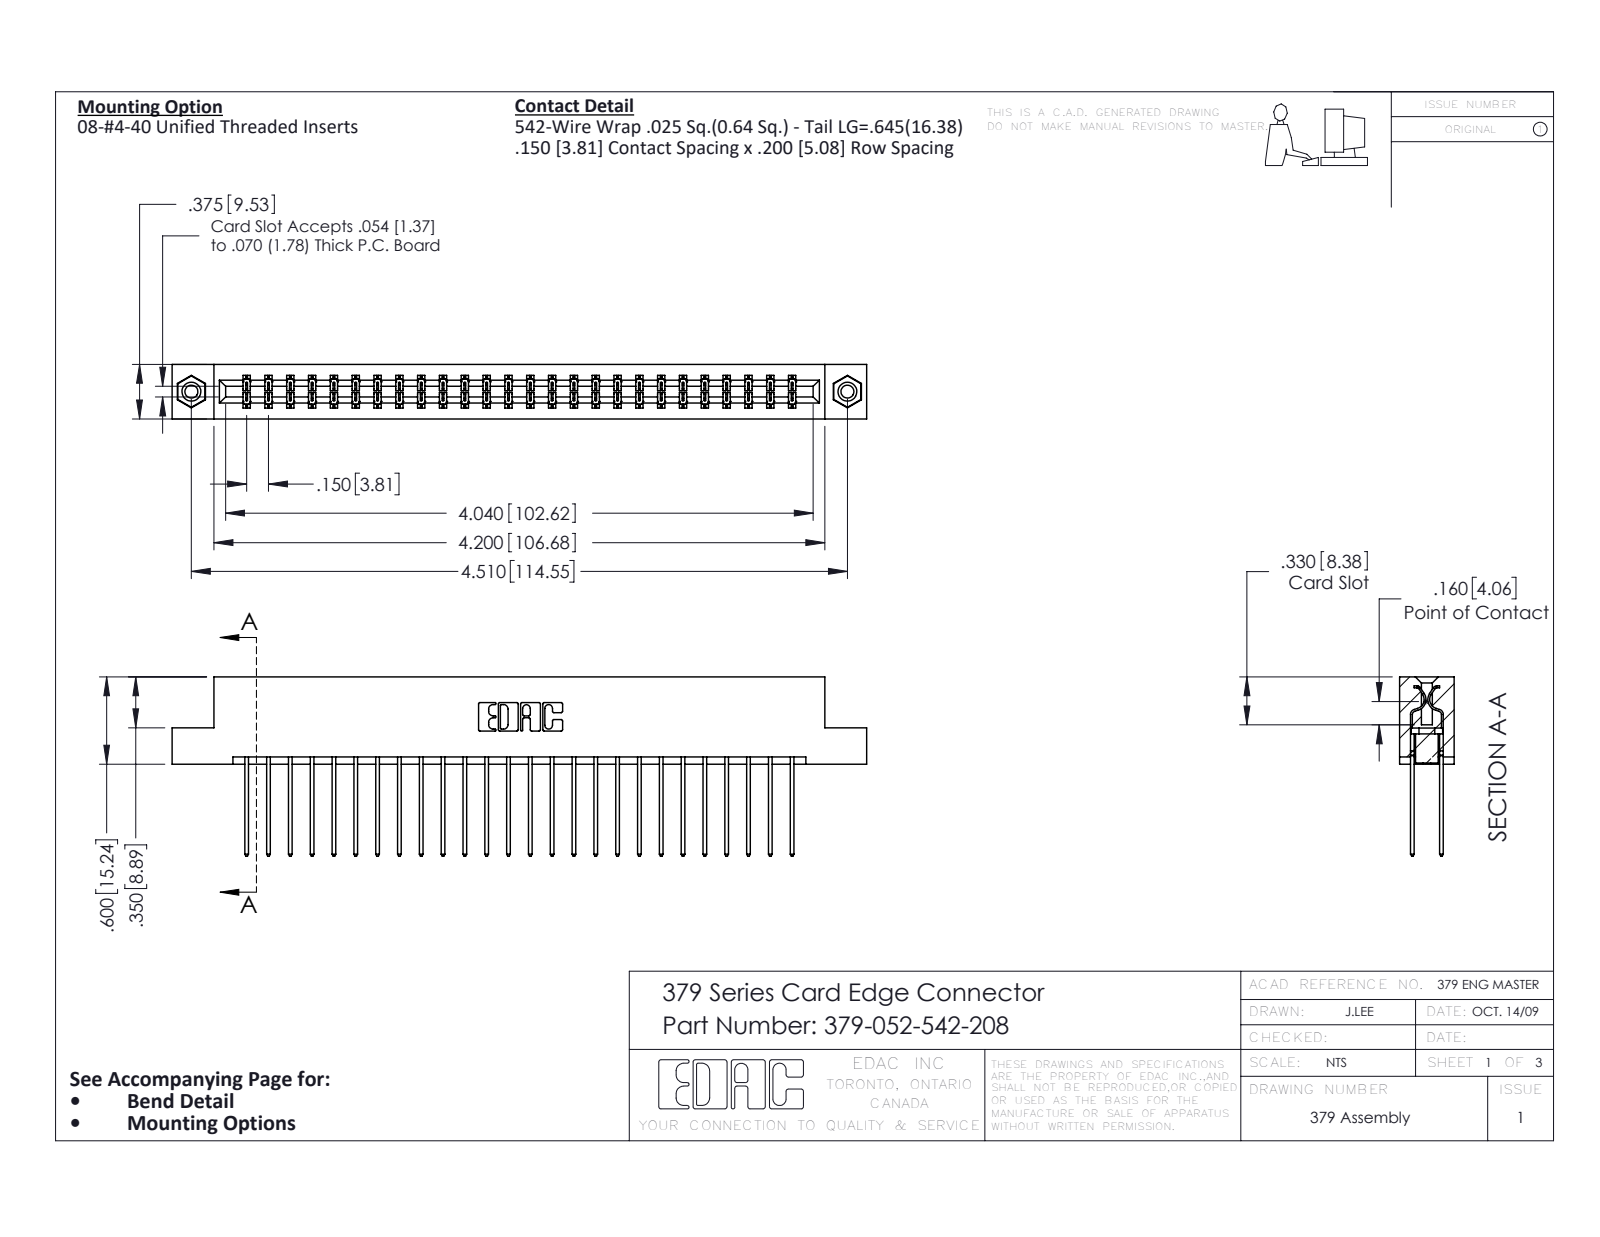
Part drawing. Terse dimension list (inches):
name: 379-052-542-208; 379 Part_Flush - .156 Dia - TI; 345-292-001_345-293-142; 345-250-001_345-250-003-102
written by: SolidWorks 2016 (CONFIG_CONTROL_DESIGN)
unit: in
bodies: 55 solids, 2878 faces (1974 planar, 888 cylindrical, 16 other)
size: 4.775 × 1.232 × 0.375
volume: 0.791 in³; area: 24.24 in²
holes: 2× ⌀0.089, 2× ⌀0.125, 2× ⌀0.156
bosses: 2× ⌀0.155
rounds: 78× R0.006, 52× R0.01, 22× R0.01, 6× R0.007, 6× R0.031, 3× R0.026, 2× R0.014, 2× R0.022
face distances: 0.3, 0.075, 0.375, 0.2, 0.1, 0.275, 0.025, 0.076, 0.15, 0.225
hole spacings: 4.51
